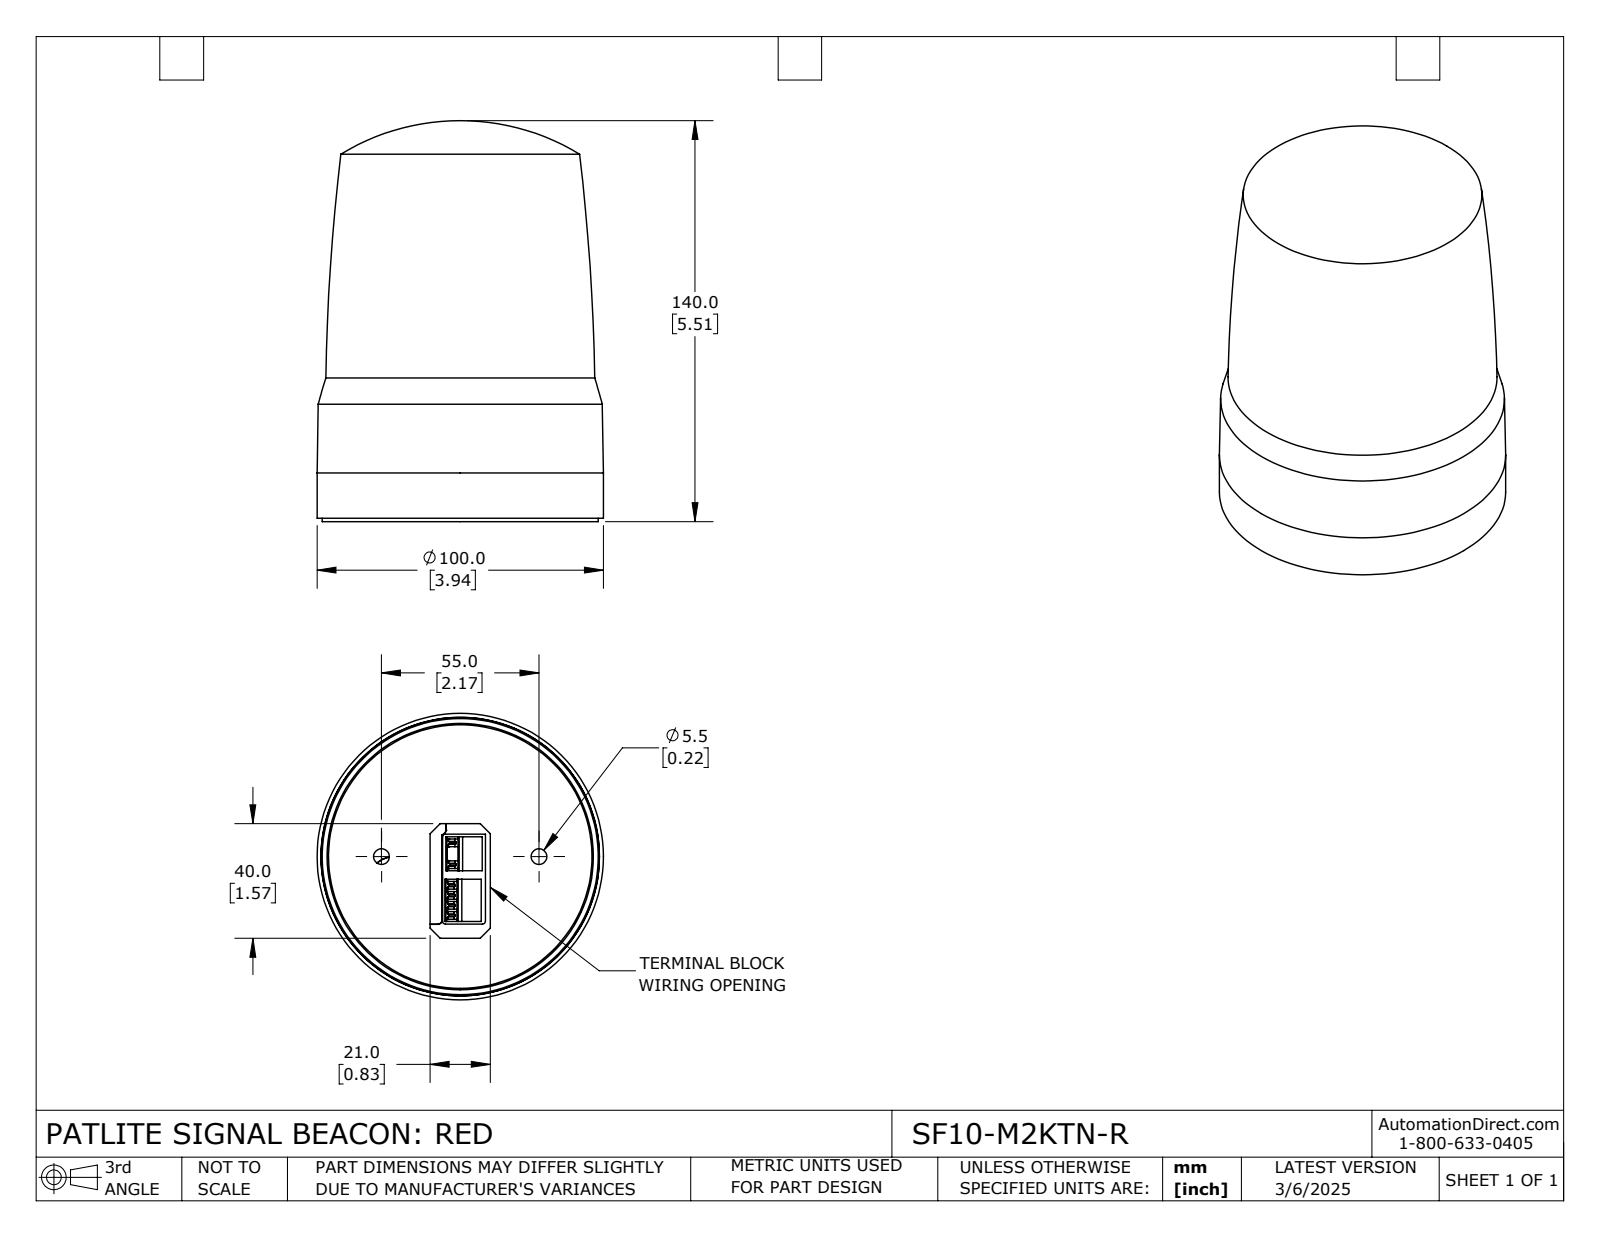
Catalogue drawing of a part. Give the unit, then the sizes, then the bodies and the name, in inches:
Units: inches
Overall size (bounding box): 5.512 × 3.937 × 3.937
Round holes (diameter × count): ⌀0.217 ×2, ⌀0.512 ×2, ⌀3.661 ×1, ⌀3.764 ×1
Round bosses / shafts (diameter × count): ⌀3.937 ×1, ⌀3.795 ×1, ⌀3.72 ×1, ⌀3.669 ×1, ⌀3.622 ×1
Partial cylindrical surfaces — rounded edges, fillets, slot ends (radius × count): R0.012 ×2, R1.745 ×1, R1.762 ×1
Main face-to-face distances: 0.248, 0.579, 0.331, 0.059, 0.272, 0.52, 0.496, 0.124, 0.173, 0.276
Hole centre spacings: 1.083, 2.165
Volume: 52.34 in³ · Surface area: 119.3 in²
Bodies: 2 solids, 268 faces (183 planar, 29 cylindrical, 56 other)
Part name (STEP PRODUCT): SF10-M2KTN-R
STEP written by: SolidWorks 2024 (CONFIG_CONTROL_DESIGN)
